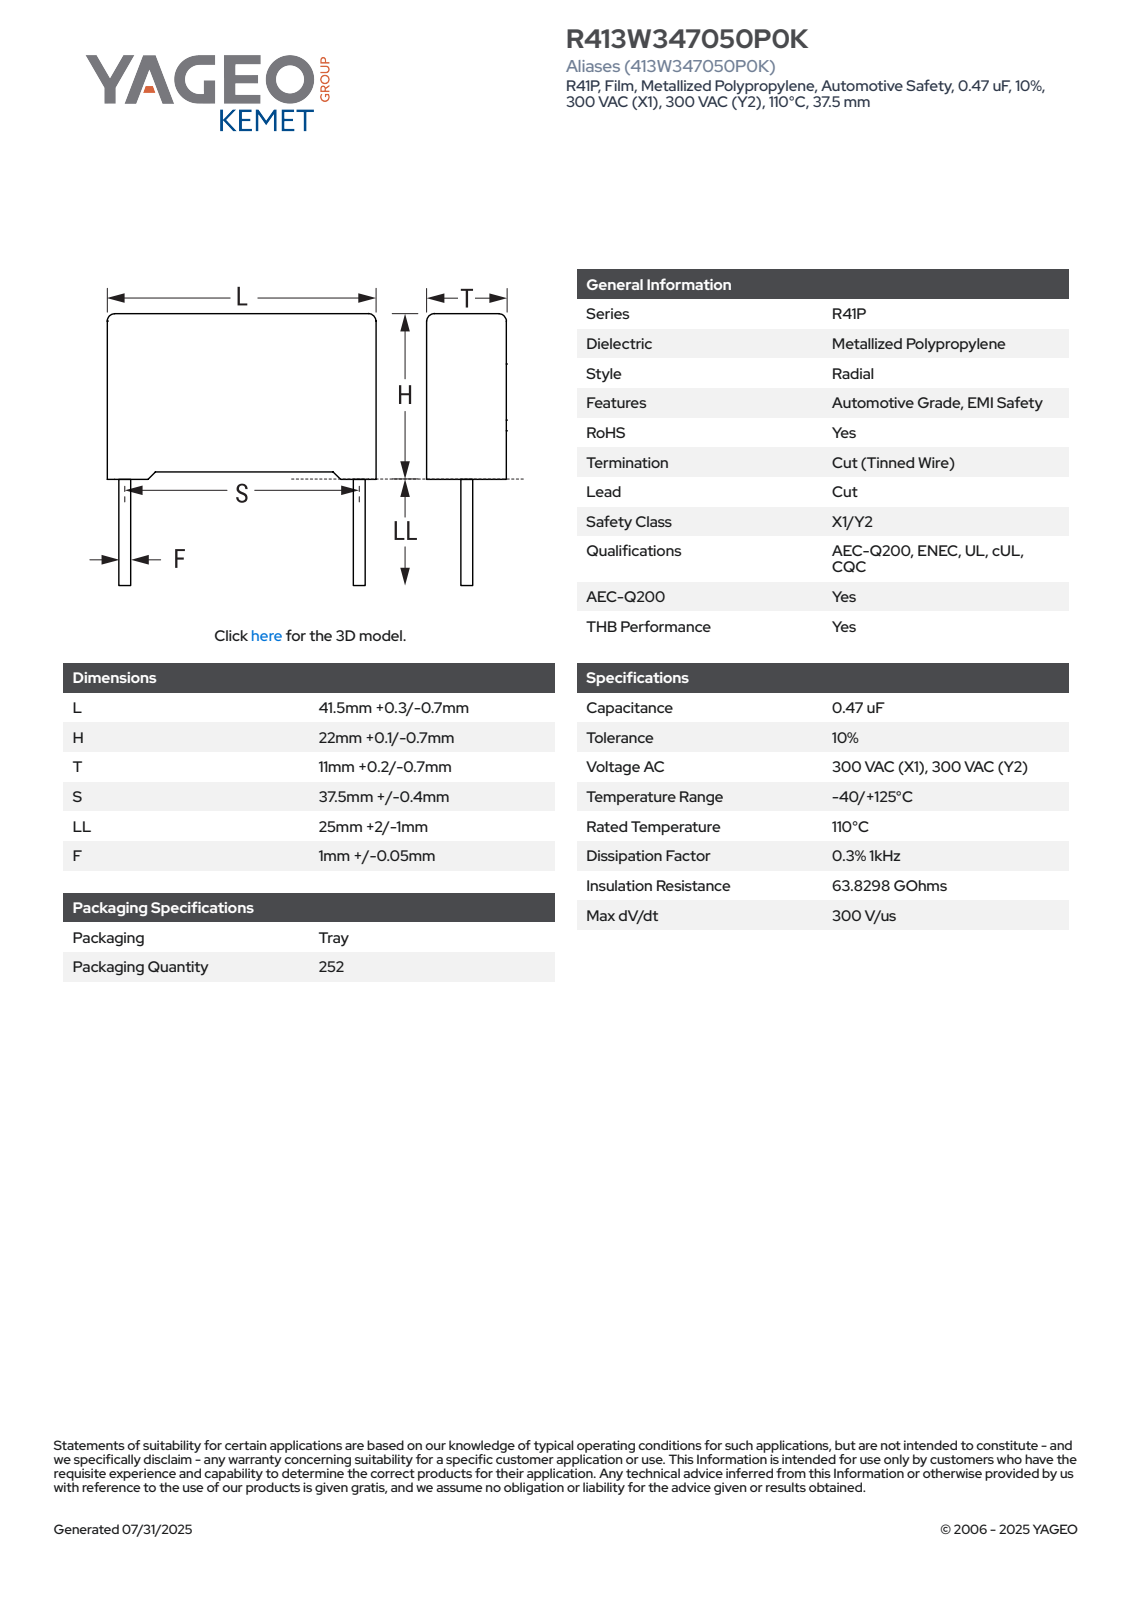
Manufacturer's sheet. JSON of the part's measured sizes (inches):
{"part_name": "CFR_RB2_41.5X22X11_L41.8H22.1T11.2S37.5LL27F1.05", "step_written_by": "SolidWorks 2021 (AUTOMOTIVE_DESIGN)", "units": "inches", "bodies": {"solids": 4, "faces": 85, "planar": 77, "cylindrical": 8, "other": 0}, "overall_size": [1.933, 1.646, 0.441], "volume_in3": 0.614, "surface_area_in2": 5.489, "round_bosses_or_shafts": [[0.041, 2]], "partial_cylinders_radius": [[0.02, 4]], "face_to_face_distances": [0.441, 0.84, 1.646, 0.841, 0.03, 0.03, 0.87, 0.441, 0.055, 1.591]}
